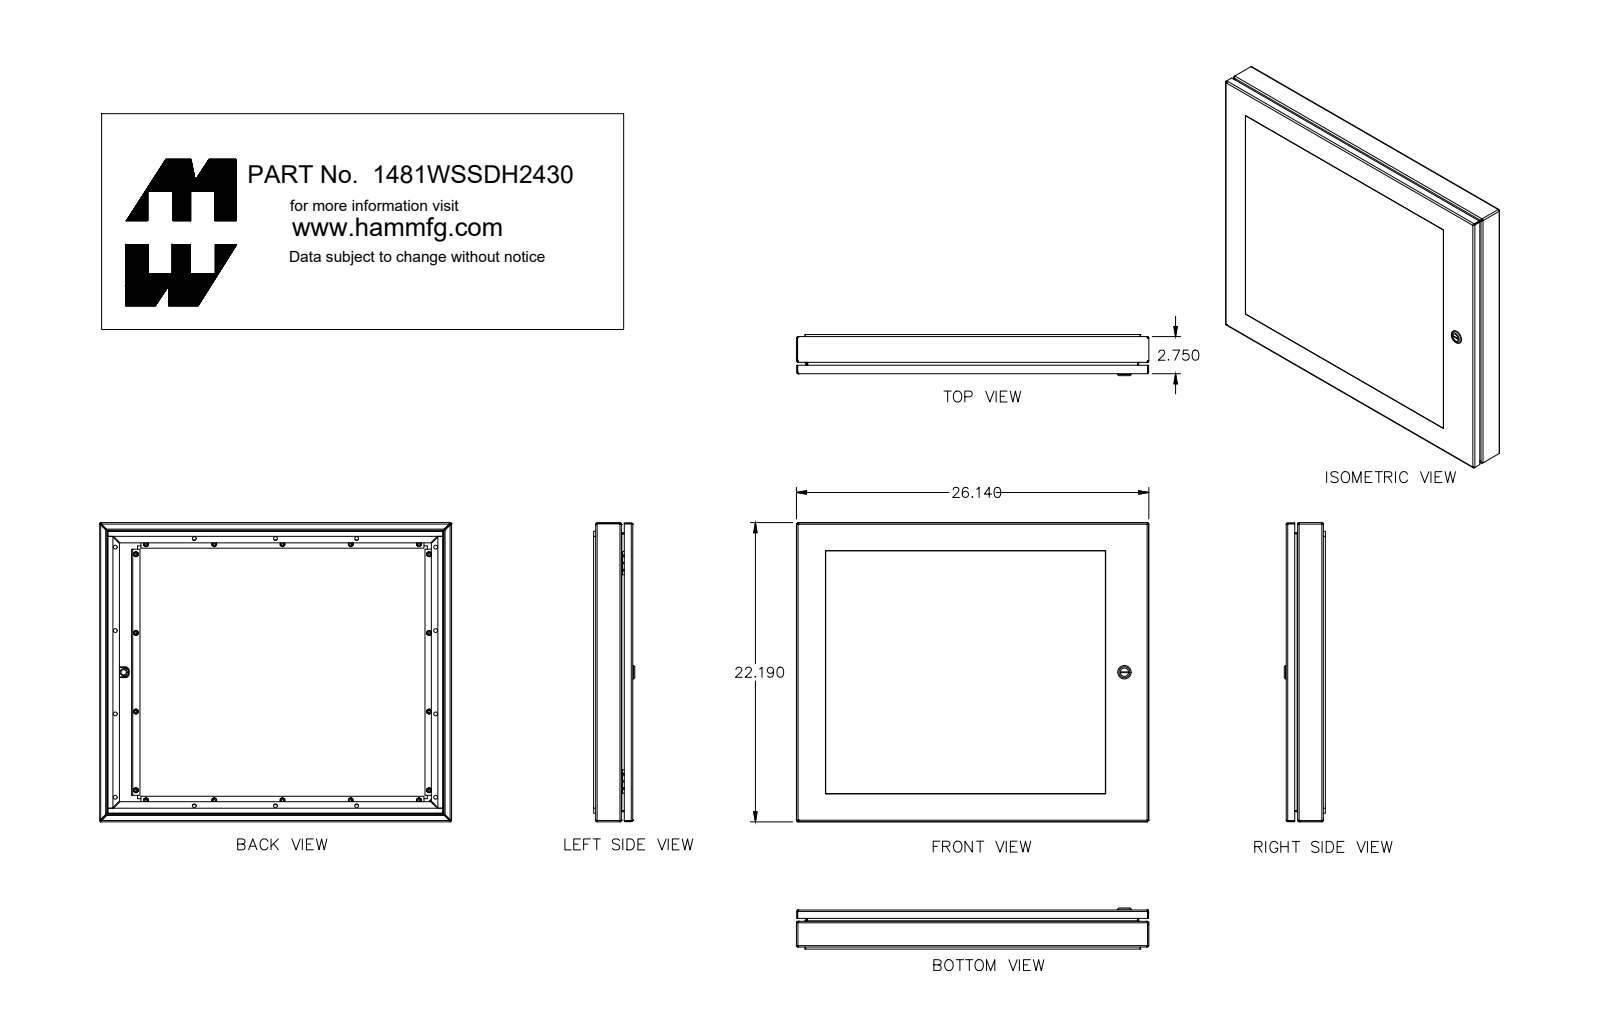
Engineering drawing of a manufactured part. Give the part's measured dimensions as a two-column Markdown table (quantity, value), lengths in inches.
| quantity | value |
| --- | --- |
| part name | 1481WSSDH2430_Default |
| STEP written by | SolidWorks 2019 (CONFIG_CONTROL_DESIGN) |
| units | inches |
| bodies | 58 solids, 1307 faces (693 planar, 382 cylindrical, 232 other) |
| overall size | 26.14 × 22.19 × 2.91 |
| volume | 151.9 in³ |
| surface area | 2 415 in² |
| round holes (diameter × count) | 0.13 × 18, 0.281 × 14, 0.136 × 2, 0.197 × 1, 0.24 × 1, 0.242 × 1, 0.387 × 1, 0.5 × 1, 0.63 × 1, 0.768 × 1 |
| round bosses / shafts (diameter × count) | 0.368 × 18, 0.226 × 18, 0.164 × 18, 1.1 × 1, 0.785 × 1, 0.625 × 1, 0.525 × 1, 0.477 × 1 |
| partial cylindrical surfaces (radius × count) | 0.101 × 36, 0.036 × 28, 0.108 × 28, 0.016 × 4, 0.088 × 4, 0.125 × 2, 0.021 × 1, 0.029 × 1 |
| main face-to-face distances | 0.072, 0.25, 0.178, 2.578, 2.328, 0.842, 1.736, 0.592, 22.118, 2.65 |
| hole center spacings | 19.663, 5.063, 24.555, 22.519, 5.687, 5.833, 6.182, 6.23 |
